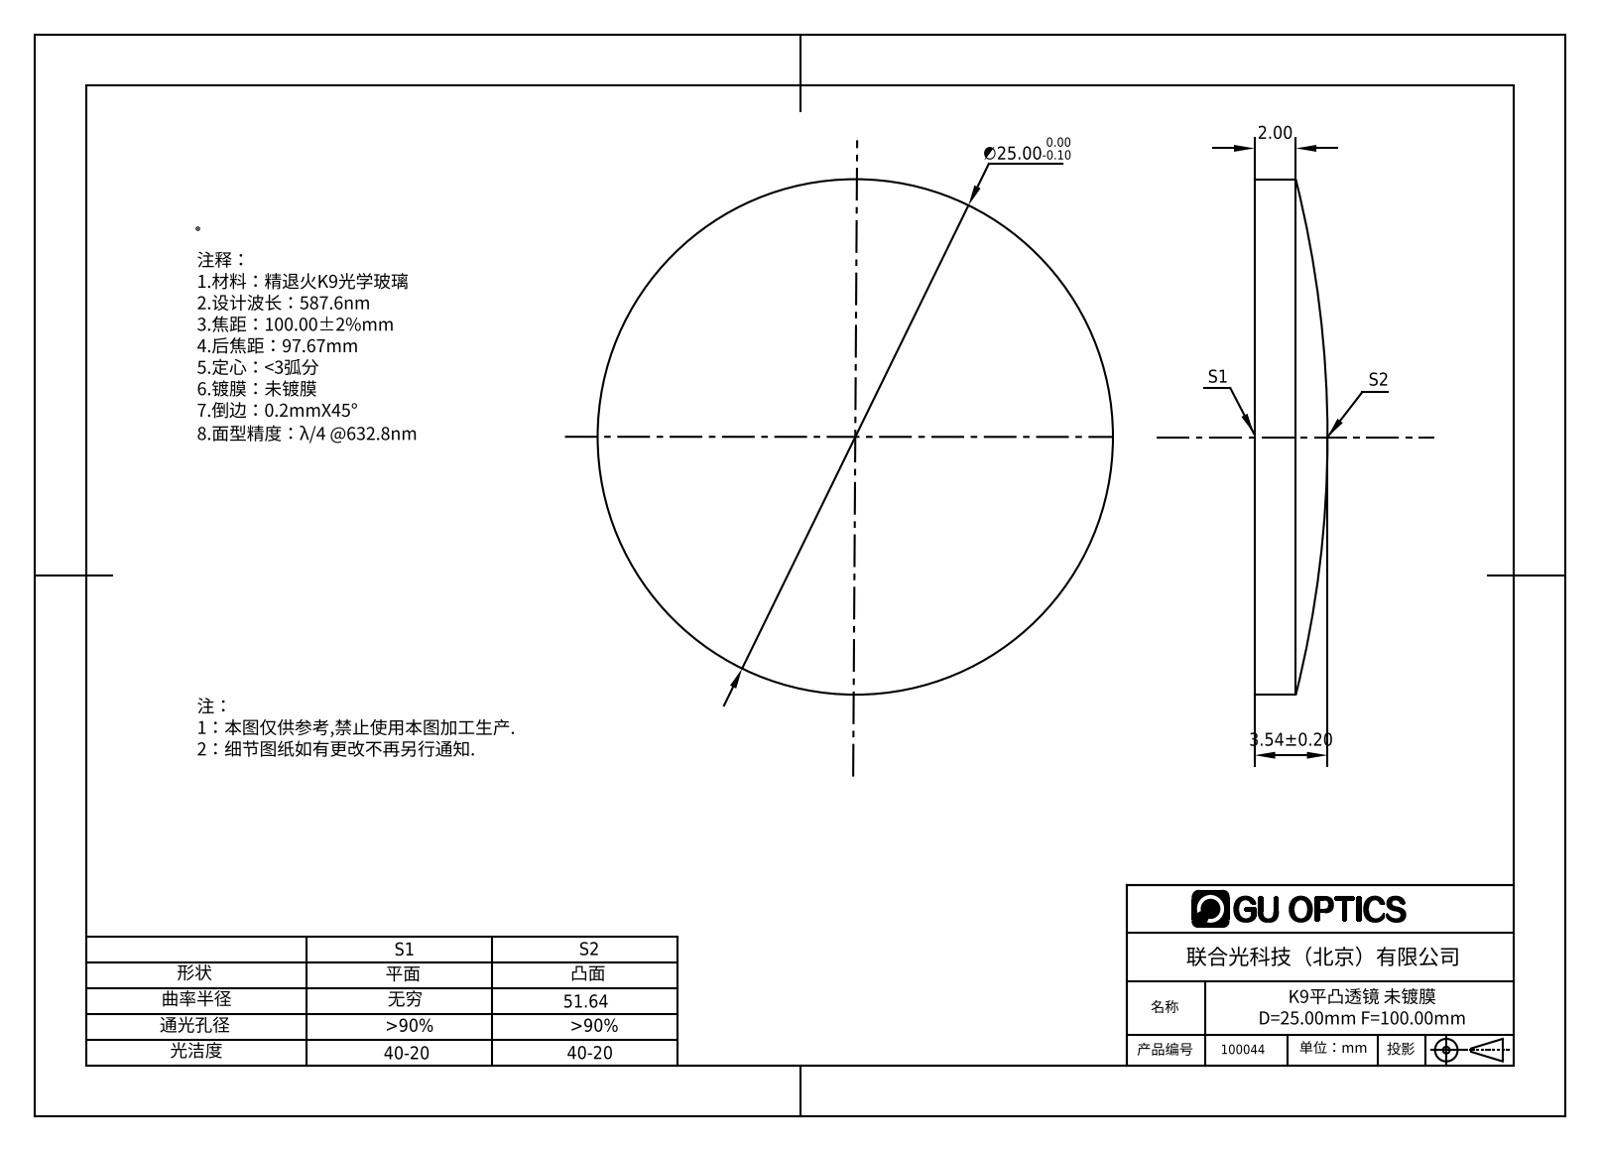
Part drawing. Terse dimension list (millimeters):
name: 100044
written by: SolidWorks 2016 (AUTOMOTIVE_DESIGN)
unit: mm
bodies: 1 solid, 5 faces (1 planar, 2 cylindrical, 2 other)
size: 25 × 25 × 3.54
volume: 1 362 mm³; area: 1 146 mm²
bosses: 1× ⌀25
